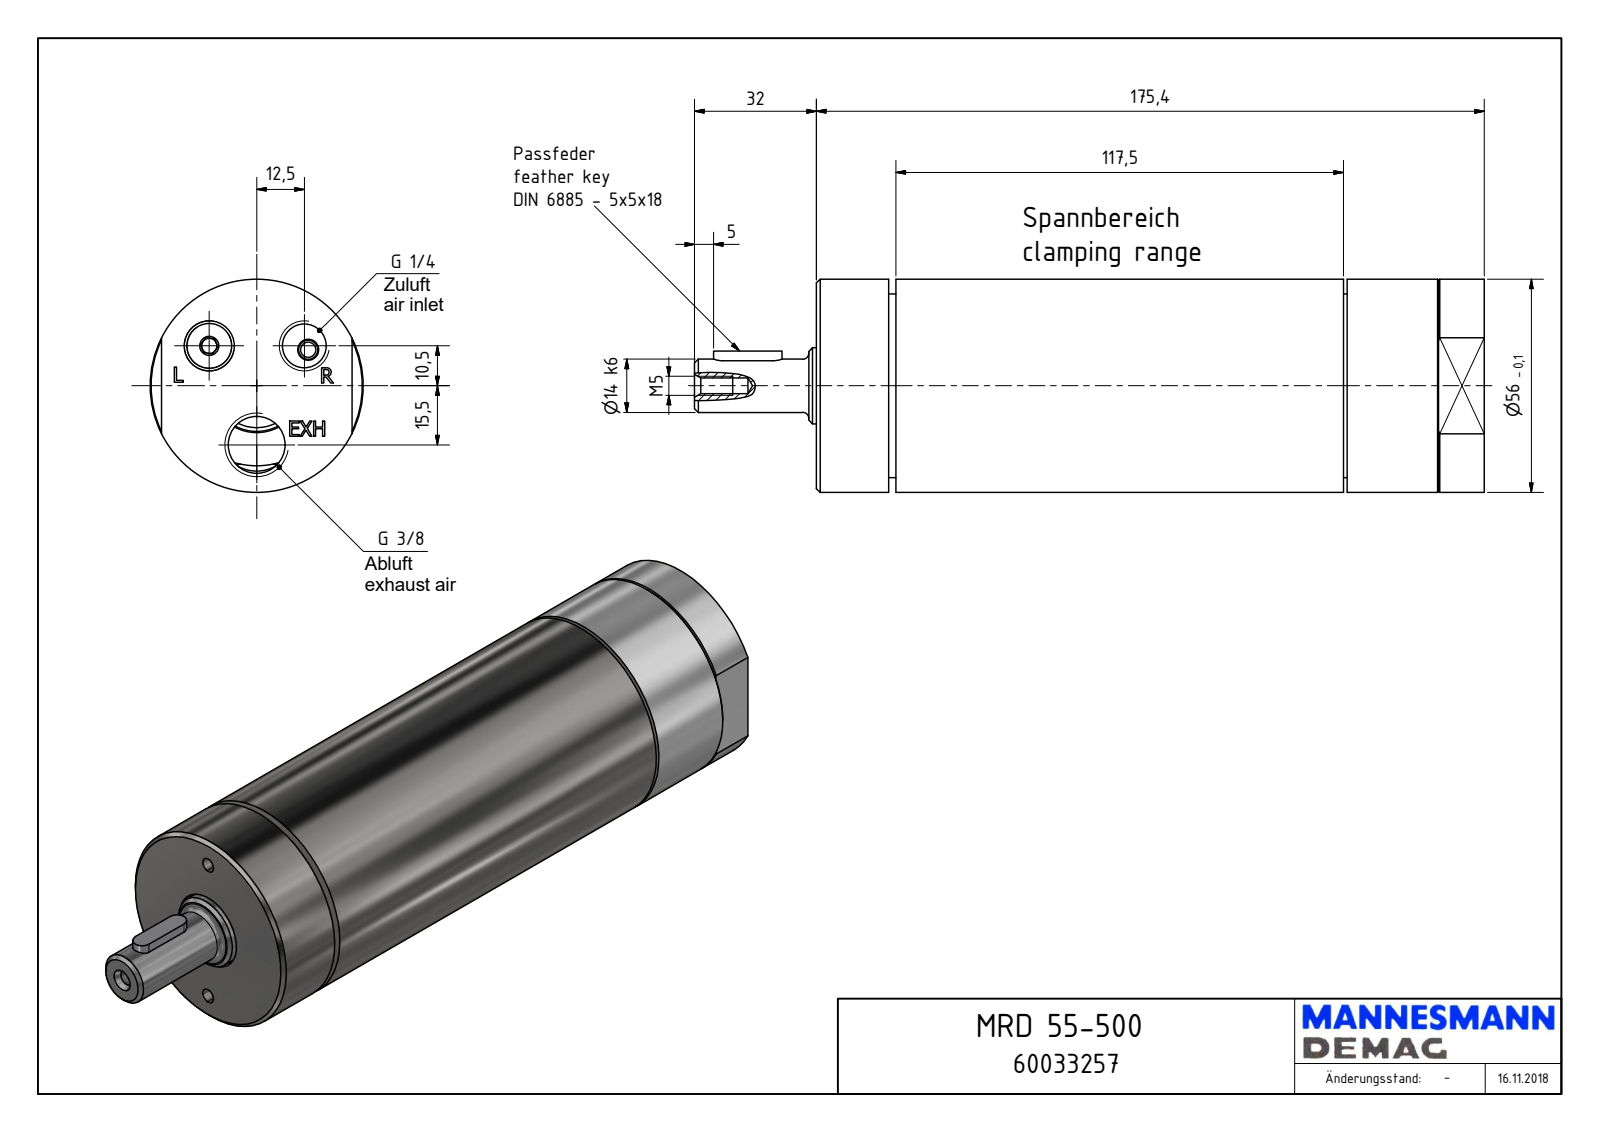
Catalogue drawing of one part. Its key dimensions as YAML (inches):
part_name: "MRD 55-500_60033257"
step_written_by: "Autodesk Inventor 2018 (AUTOMOTIVE_DESIGN)"
units: inches
bodies: {solids: 1, faces: 181, planar: 107, cylindrical: 31, other: 43}
overall_size: [8.165, 2.205, 2.205]
volume: 26.27
surface_area: 67.81
round_holes:
  - {diameter: 0.157, count: 3}
  - {diameter: 0.163, count: 1}
  - {diameter: 0.451, count: 1}
  - {diameter: 0.589, count: 1}
  - {diameter: 0.827, count: 1}
  - {diameter: 0.837, count: 1}
  - {diameter: 0.927, count: 1}
  - {diameter: 1.024, count: 1}
  - {diameter: 1.905, count: 1}
round_bosses_or_shafts:
  - {diameter: 2.205, count: 1}
  - {diameter: 1.897, count: 1}
  - {diameter: 0.785, count: 1}
  - {diameter: 0.551, count: 1}
partial_cylinders:
  - {radius: 0.098, count: 2}
  - {radius: 0.236, count: 2}
  - {radius: 0.225, count: 1}
  - {radius: 0.772, count: 1}
  - {radius: 0.906, count: 1}
face_to_face_distances: [6.906, 0.823, 6.083, 5.449, 4.626, 1.457, 5.488, 0.748, 0.075, 4.701]
hole_center_spacings: [0.643, 0.827, 1.136, 1.334, 0.217, 0.61, 0.984, 1.437]
